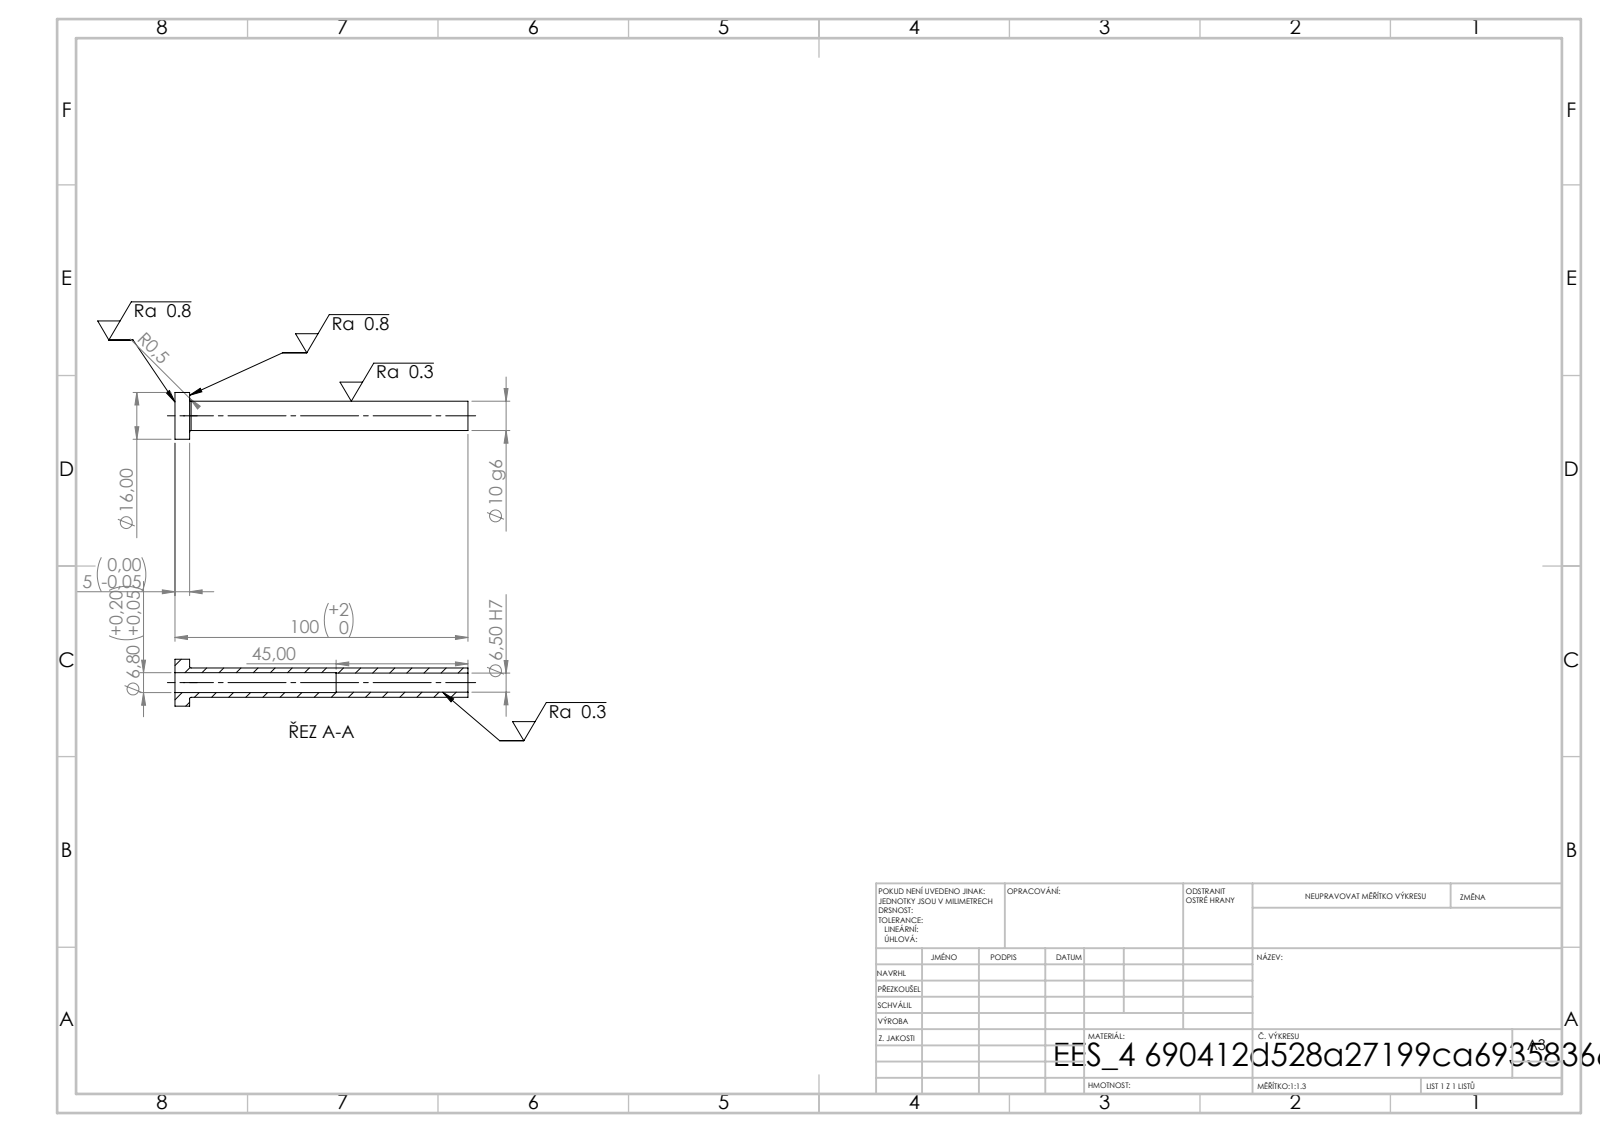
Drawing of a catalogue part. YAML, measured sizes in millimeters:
step_written_by: "SolidWorks 2019 (CONFIG_CONTROL_DESIGN)"
units: millimeters
bodies: {solids: 1, faces: 14, planar: 4, cylindrical: 8, other: 2}
overall_size: [100, 16, 16]
volume: 4978
surface_area: 5659
round_holes:
  - {diameter: 6.5, count: 1}
  - {diameter: 6.8, count: 1}
round_bosses_or_shafts:
  - {diameter: 16, count: 1}
  - {diameter: 10, count: 1}
face_to_face_distances: [5, 100, 95, 55, 50, 45]
